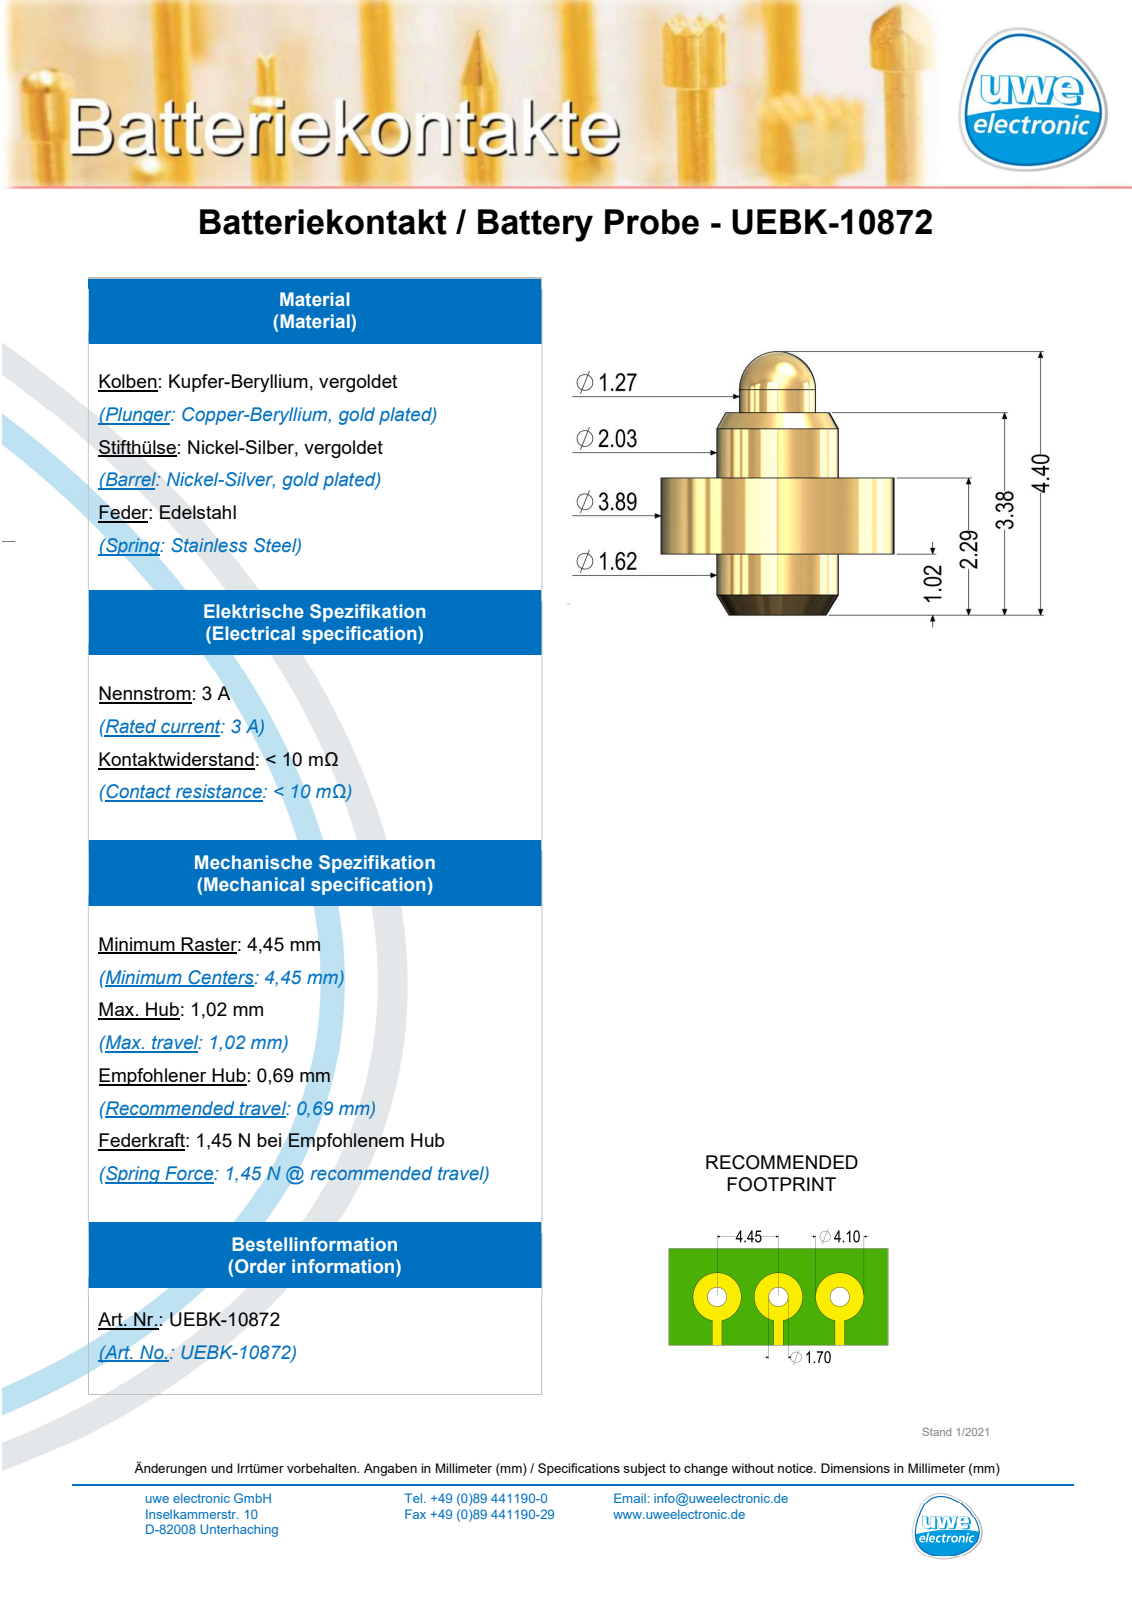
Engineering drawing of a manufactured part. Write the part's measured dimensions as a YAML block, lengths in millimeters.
part_name: "uebk-10872"
step_written_by: "SolidWorks 2017 (AUTOMOTIVE_DESIGN)"
units: millimeters
bodies: {solids: 1, faces: 18, planar: 4, cylindrical: 8, other: 6}
overall_size: [4.4, 3.89, 3.89]
volume: 23
surface_area: 54
round_bosses_or_shafts:
  - {diameter: 3.89, count: 1}
  - {diameter: 2.03, count: 1}
  - {diameter: 1.27, count: 1}
face_to_face_distances: [1.27, 1.02, 2.29, 3.38, 2.36, 1.09]
